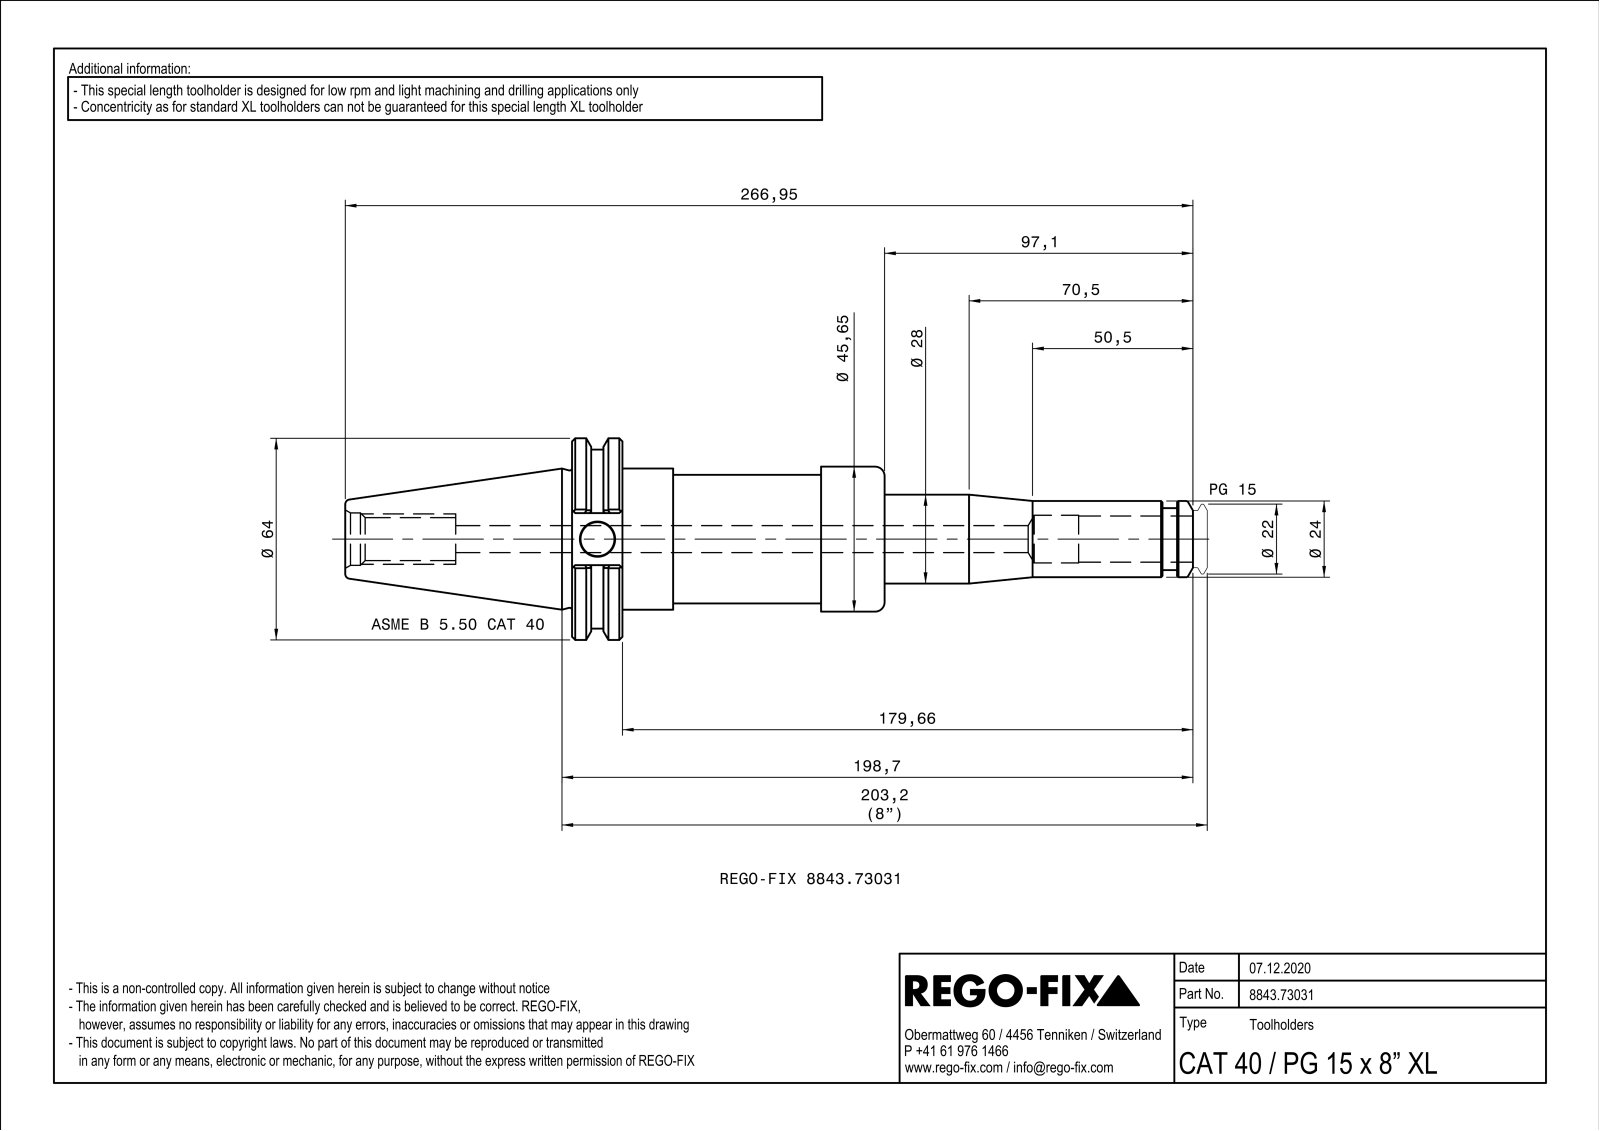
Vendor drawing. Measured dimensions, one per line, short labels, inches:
name: NOCUT
written by: SIEMENS PLM Software Solid Edge ST10 (AUTOMOTIVE_DESIGN)
unit: in
bodies: 1 solid, 157 faces (47 planar, 36 cylindrical, 74 other)
size: 10.51 × 2.5 × 2.393
volume: 14.33 in³; area: 83.15 in²
holes: 1× ⌀0.354, 1× ⌀0.394, 1× ⌀0.421, 1× ⌀0.512, 1× ⌀0.533, 1× ⌀0.591, 1× ⌀0.65, 1× ⌀0.984, 1× ⌀1.142, 1× ⌀1.511, 1× ⌀1.577, 1× ⌀1.705
bosses: 1× ⌀2.5, 1× ⌀2.219, 1× ⌀1.797, 1× ⌀1.75, 1× ⌀1.594, 1× ⌀1.575, 1× ⌀1.339, 1× ⌀1.299
rounds: 4× R0.02, 1× R0.896
face distances: 0.625, 3.25, 3.875, 0.236, 0.551, 0.059, 3.191, 3.816, 0.787, 0.728
